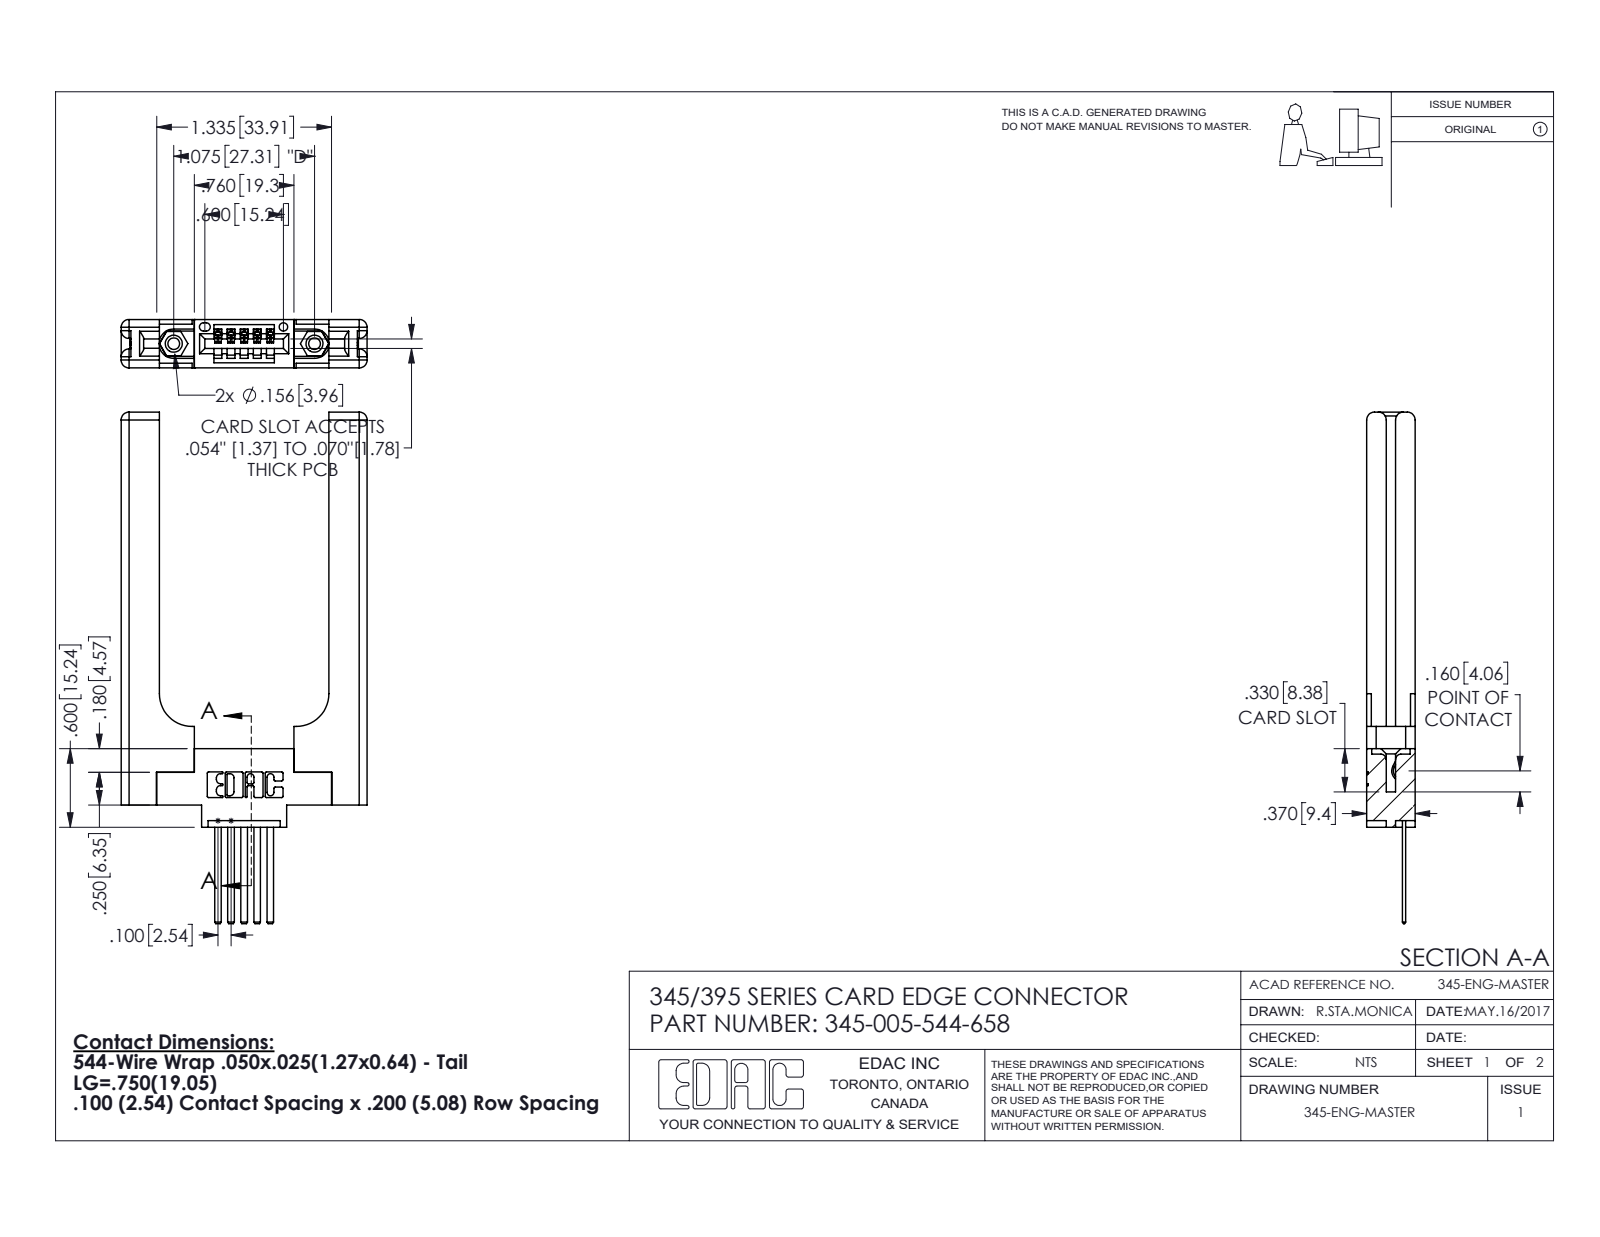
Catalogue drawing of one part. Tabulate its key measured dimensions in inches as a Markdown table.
| quantity | value |
| --- | --- |
| part name | 345-220-058_345-220-058; 345-005-544-658; 345 Part_0.170 Offset - 0.156 Dia-TH; 345-250-001_345-250-001-102 (+1 more) |
| STEP written by | SolidWorks 2016 (CONFIG_CONTROL_DESIGN) |
| units | inches |
| bodies | 10 solids, 646 faces (412 planar, 174 cylindrical, 60 other) |
| overall size | 3.907 × 1.879 × 0.37 |
| volume | 0.774 in³ |
| surface area | 16.51 in² |
| round holes (diameter × count) | 0.089 × 2, 0.125 × 2, 0.156 × 2, 0.064 × 1 |
| round bosses / shafts (diameter × count) | 0.155 × 2 |
| partial cylindrical surfaces (radius × count) | 0.01 × 22, 0.06 × 16, 0.006 × 10, 0.007 × 6, 0.031 × 6, 0.026 × 3, 0.03 × 2, 0.031 × 2 |
| main face-to-face distances | 0.37, 0.15, 0.22, 0.072, 0.148, 0.077, 0.298, 1.296, 0.071, 0.292 |
| hole center spacings | 0.27, 0.847, 1.075 |
